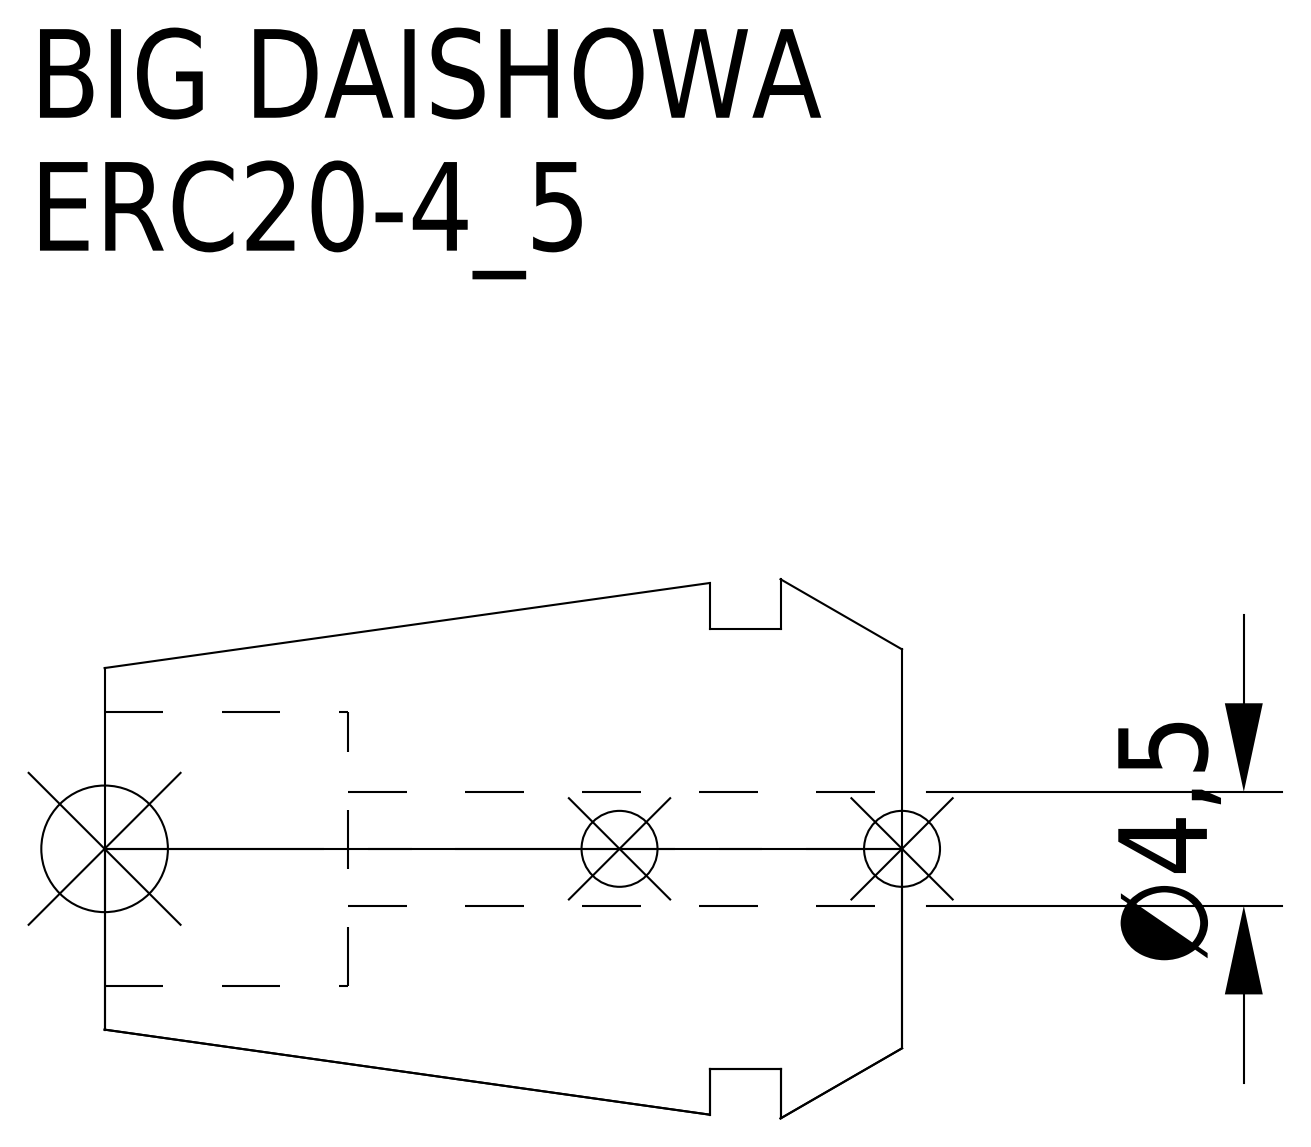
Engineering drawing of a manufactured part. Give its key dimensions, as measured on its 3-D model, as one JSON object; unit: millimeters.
{"part_name": "ERC20-4_5", "step_written_by": "CREO PARAMETRIC BY PTC INC, 2016380 (AUTOMOTIVE_DESIGN)", "units": "millimeters", "bodies": {"solids": 1, "faces": 15, "planar": 5, "cylindrical": 6, "other": 4}, "overall_size": [31.5, 21.3, 21.3], "volume_mm3": 6653, "surface_area_mm2": 3000, "round_holes": [[4.5, 1], [10.8, 1]], "round_bosses_or_shafts": [[17.4, 1]], "face_to_face_distances": [4.8, 7.6, 2.8, 21.88, 17.08, 14.28, 31.5, 26.7, 23.9, 9.62]}
